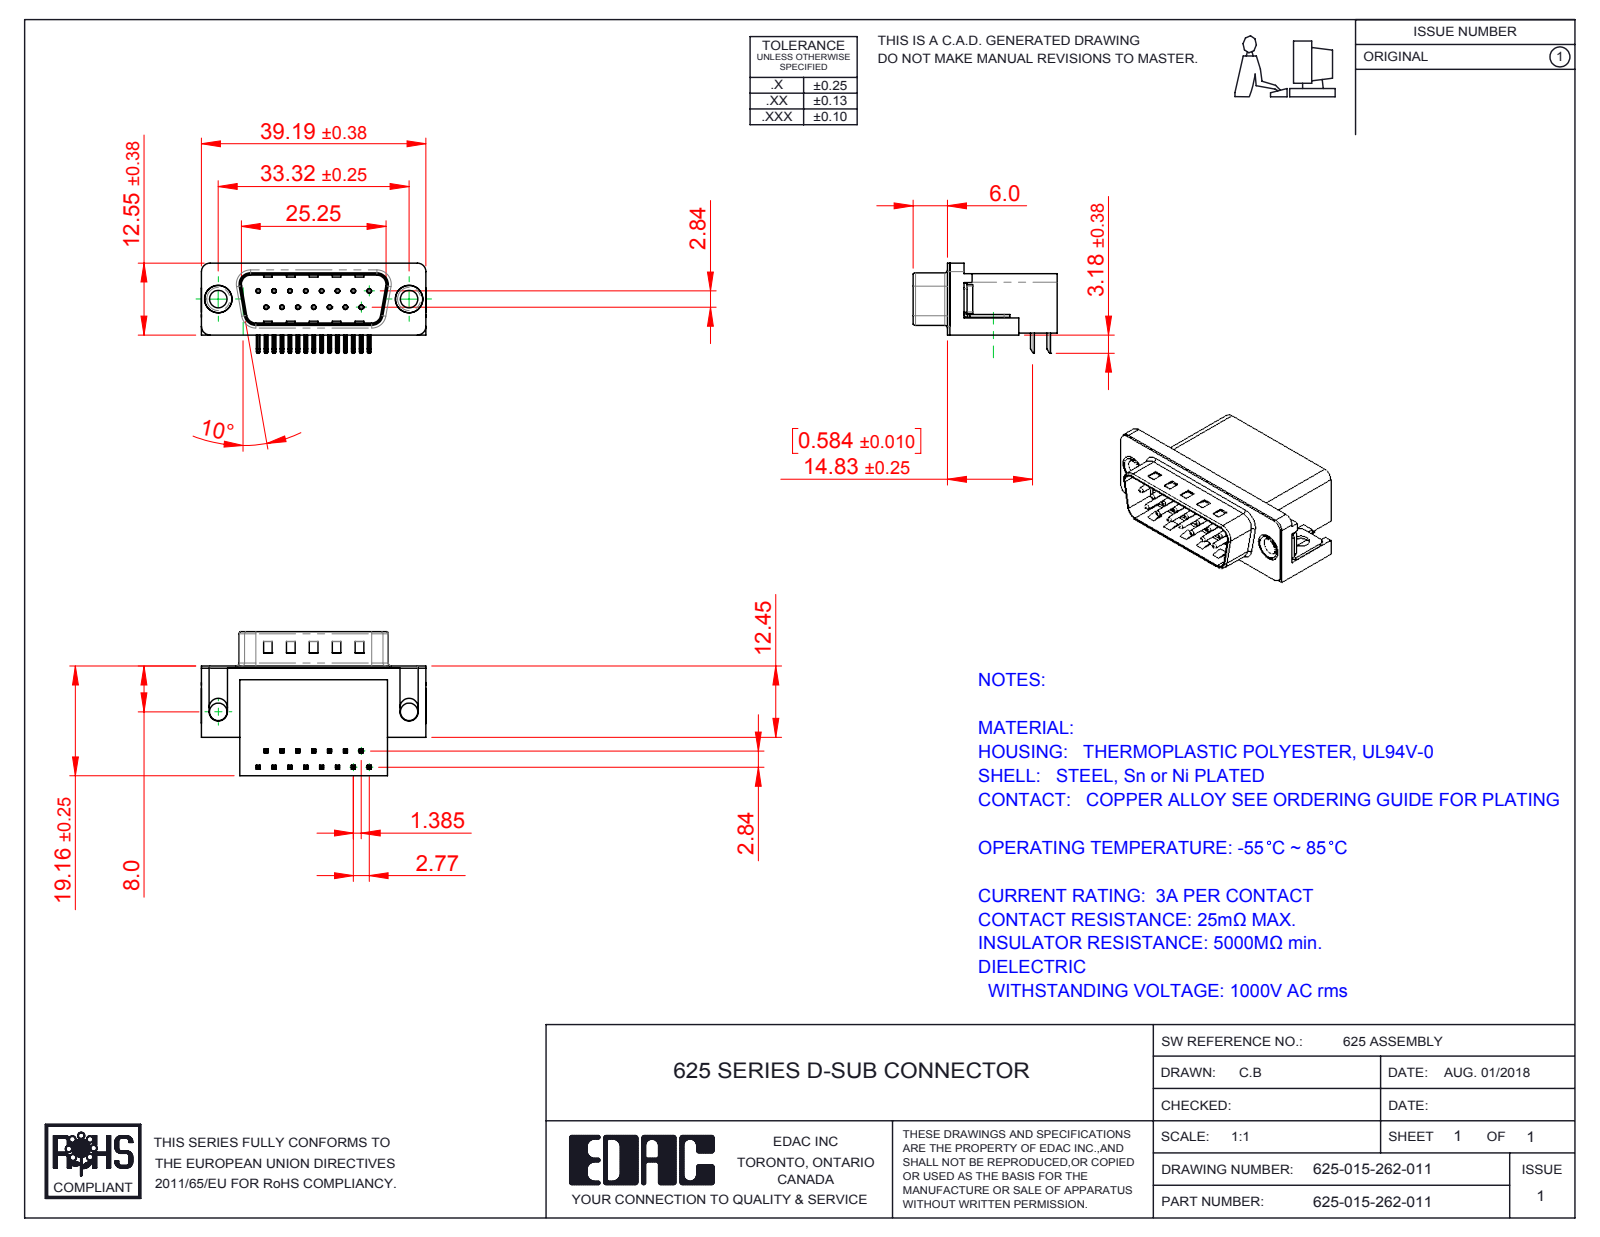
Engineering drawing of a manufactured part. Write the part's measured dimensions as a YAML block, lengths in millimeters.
part_name: "625 Contact Bottom; 625 Housing_15 Socket; 625-015-262-011; 625 Thru Hole Rivet (+3 more)"
step_written_by: "SolidWorks 2016 (CONFIG_CONTROL_DESIGN)"
units: millimeters
bodies: {solids: 21, faces: 1439, planar: 893, cylindrical: 429, other: 117}
overall_size: [39.22, 25.16, 15.73]
volume: 6228
surface_area: 6388
round_holes:
  - {diameter: 0.35, count: 15}
  - {diameter: 0.8, count: 15}
  - {diameter: 3.05, count: 4}
  - {diameter: 4, count: 2}
  - {diameter: 4.8, count: 2}
  - {diameter: 5, count: 2}
round_bosses_or_shafts:
  - {diameter: 0.75, count: 15}
  - {diameter: 4.9, count: 2}
  - {diameter: 4.75, count: 2}
  - {diameter: 3.85, count: 2}
partial_cylinders:
  - {radius: 0.25, count: 68}
  - {radius: 0.12, count: 30}
  - {radius: 1, count: 16}
  - {radius: 0.5, count: 9}
  - {radius: 1.6, count: 8}
  - {radius: 1.5, count: 6}
  - {radius: 0.9, count: 4}
  - {radius: 2, count: 4}
face_to_face_distances: [0.4, 10.35, 18.76, 2.1, 19.16, 10.46, 1.7, 10.86, 8.76, 16.26]
hole_center_spacings: [3.16, 2.77, 5.54, 8.31, 11.08, 5.03, 5.04, 7.48]
